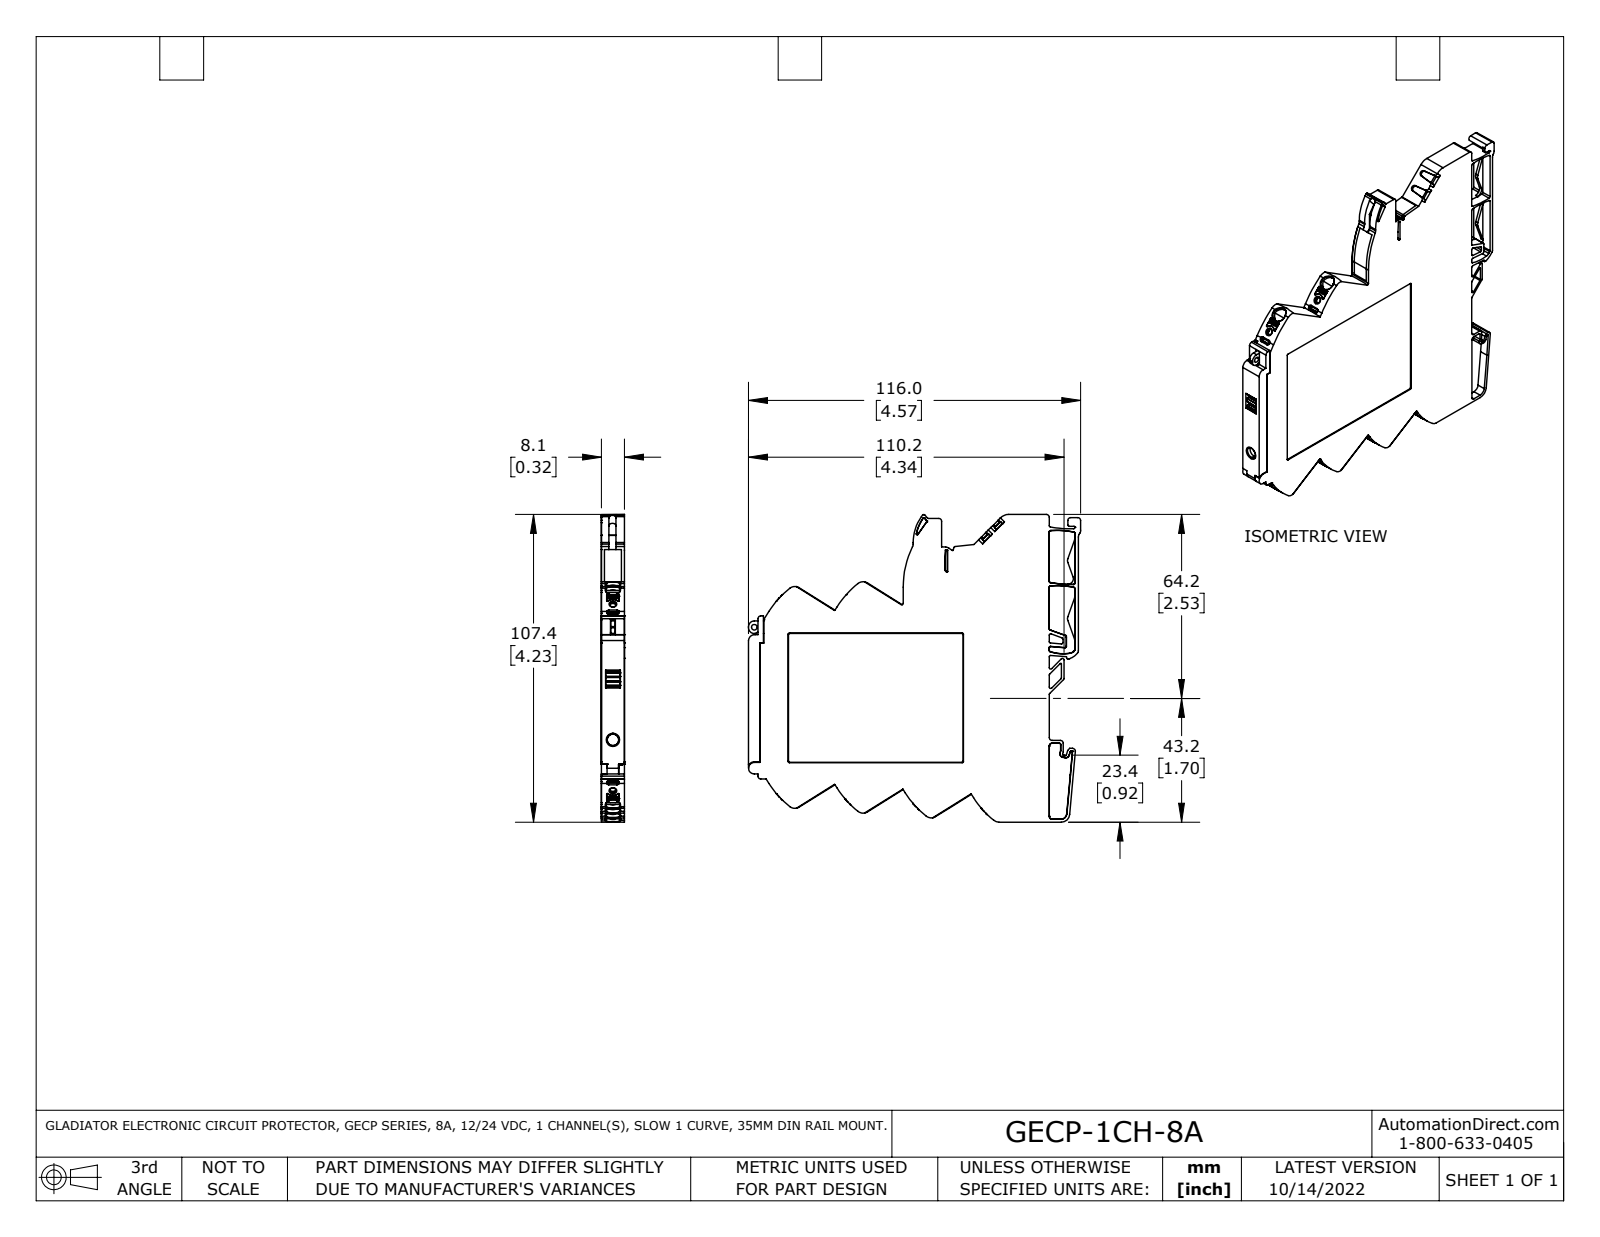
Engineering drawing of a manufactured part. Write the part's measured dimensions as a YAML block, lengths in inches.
part_name: "GECP-1CH-8A"
step_written_by: "SolidWorks 2021 (AUTOMOTIVE_DESIGN)"
units: inches
bodies: {solids: 1, faces: 1182, planar: 549, cylindrical: 466, other: 167}
overall_size: [4.567, 4.241, 0.319]
volume: 4.341
surface_area: 46.72
round_holes:
  - {diameter: 0.083, count: 6}
  - {diameter: 0.078, count: 1}
  - {diameter: 0.087, count: 1}
round_bosses_or_shafts:
  - {diameter: 0.083, count: 1}
partial_cylinders:
  - {radius: 0.02, count: 58}
  - {radius: 0.039, count: 45}
  - {radius: 0.008, count: 43}
  - {radius: 0.01, count: 28}
  - {radius: 0.012, count: 27}
  - {radius: 0.079, count: 13}
  - {radius: 0.009, count: 12}
  - {radius: 1.299, count: 12}
face_to_face_distances: [0.319, 0.311, 0.309, 0.317, 0.201, 0.157, 0.118, 0.354, 3.935, 4.093]
hole_center_spacings: [0.559, 1.118, 0.559, 1.677, 1.937]
